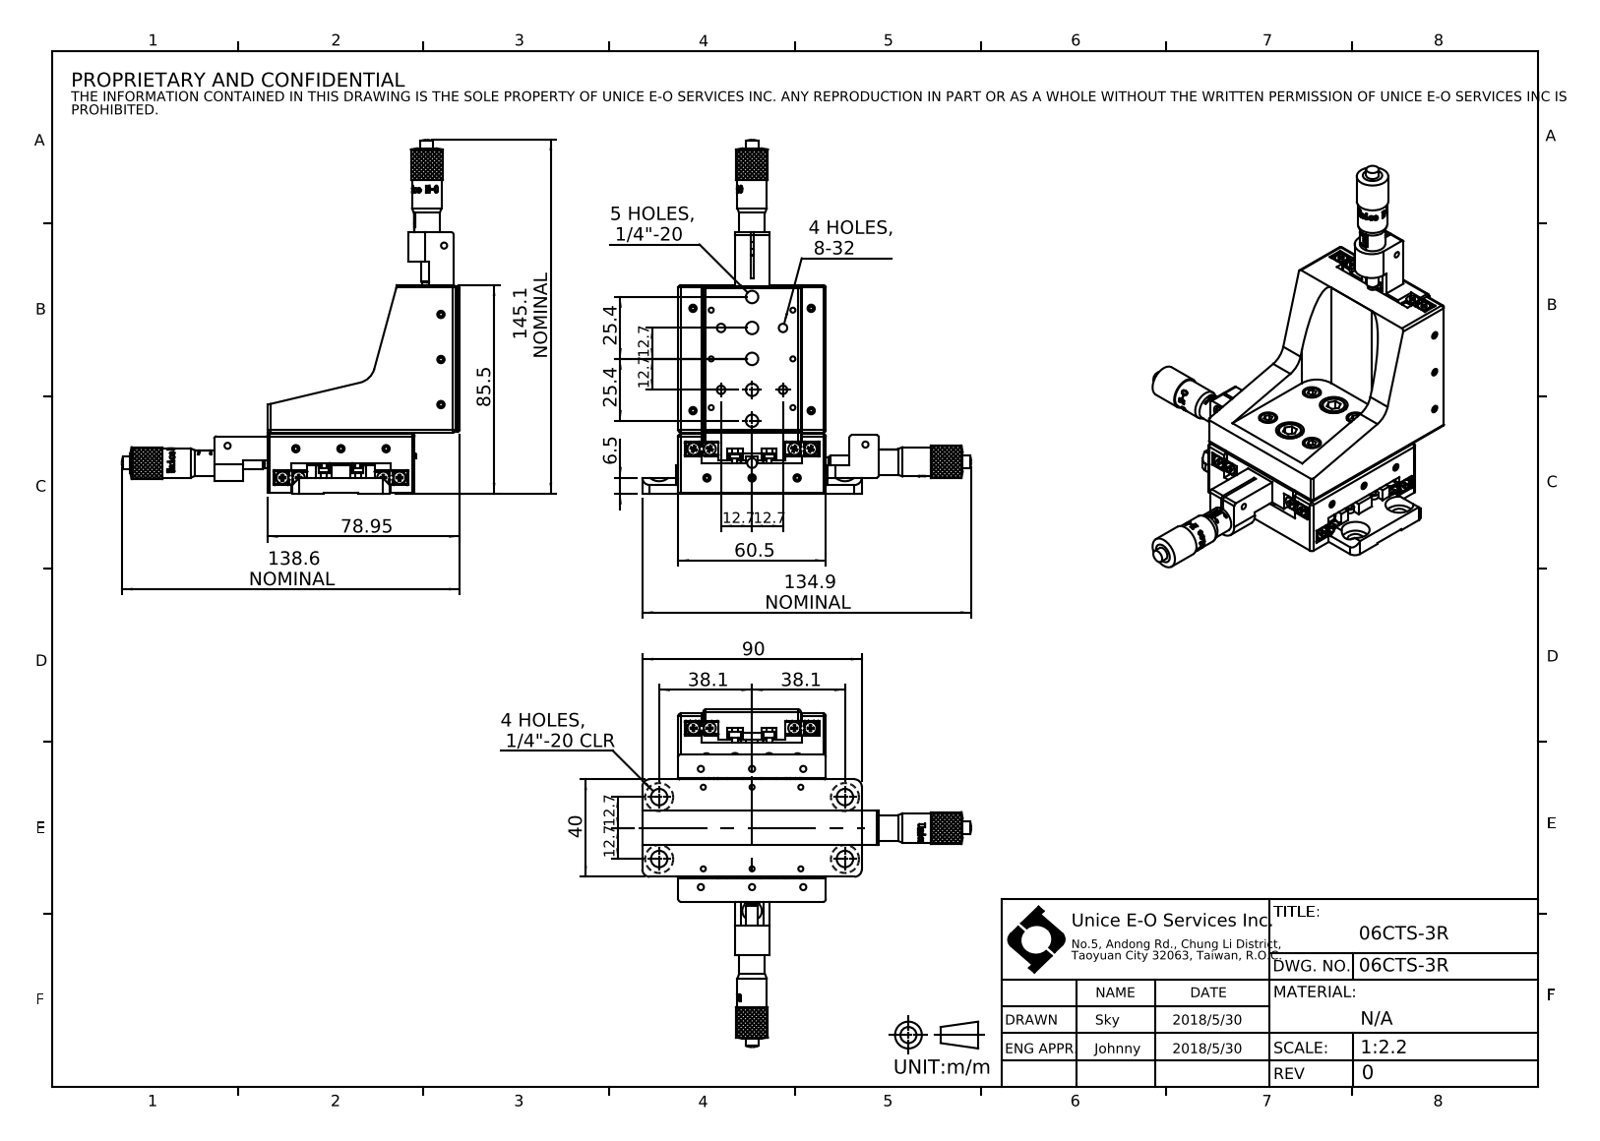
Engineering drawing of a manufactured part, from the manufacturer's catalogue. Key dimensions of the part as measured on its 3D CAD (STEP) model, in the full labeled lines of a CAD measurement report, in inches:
Part name (STEP PRODUCT): 06CTS-3R
STEP written by: SolidWorks 2016 (AUTOMOTIVE_DESIGN)
Units: inches
Bodies: 0 solids, 1318 faces (795 planar, 337 cylindrical, 186 other)
Overall size (bounding box): 5.715 × 5.457 × 5.311
Round holes (diameter × count): ⌀0.081 ×12, ⌀0.098 ×9, ⌀0.453 ×6, ⌀0.201 ×5, ⌀0.136 ×4, ⌀0.266 ×4, ⌀0.297 ×4, ⌀0.256 ×3, ⌀0.374 ×3, ⌀0.063 ×2, ⌀0.315 ×2, ⌀0.157 ×1
Round bosses / shafts (diameter × count): ⌀0.197 ×15, ⌀0.157 ×6, ⌀0.079 ×4, ⌀0.512 ×3, ⌀0.472 ×3, ⌀0.413 ×3, ⌀0.205 ×3, ⌀0.394 ×2
Partial cylindrical surfaces — rounded edges, fillets, slot ends (radius × count): R0.039 ×40, R0.118 ×6, R0.059 ×3, R0.235 ×3, R0.079 ×2, R0.276 ×2, R0.335 ×2, R0.315 ×1
Main face-to-face distances: 0.118, 0.236, 0.354, 0.65, 2.382, 0.492, 0.122, 0.472, 0.266, 0.465
Hole centre spacings: 1, 0.5, 0.329, 0.525, 0.707, 0.787, 1.118, 1.194
